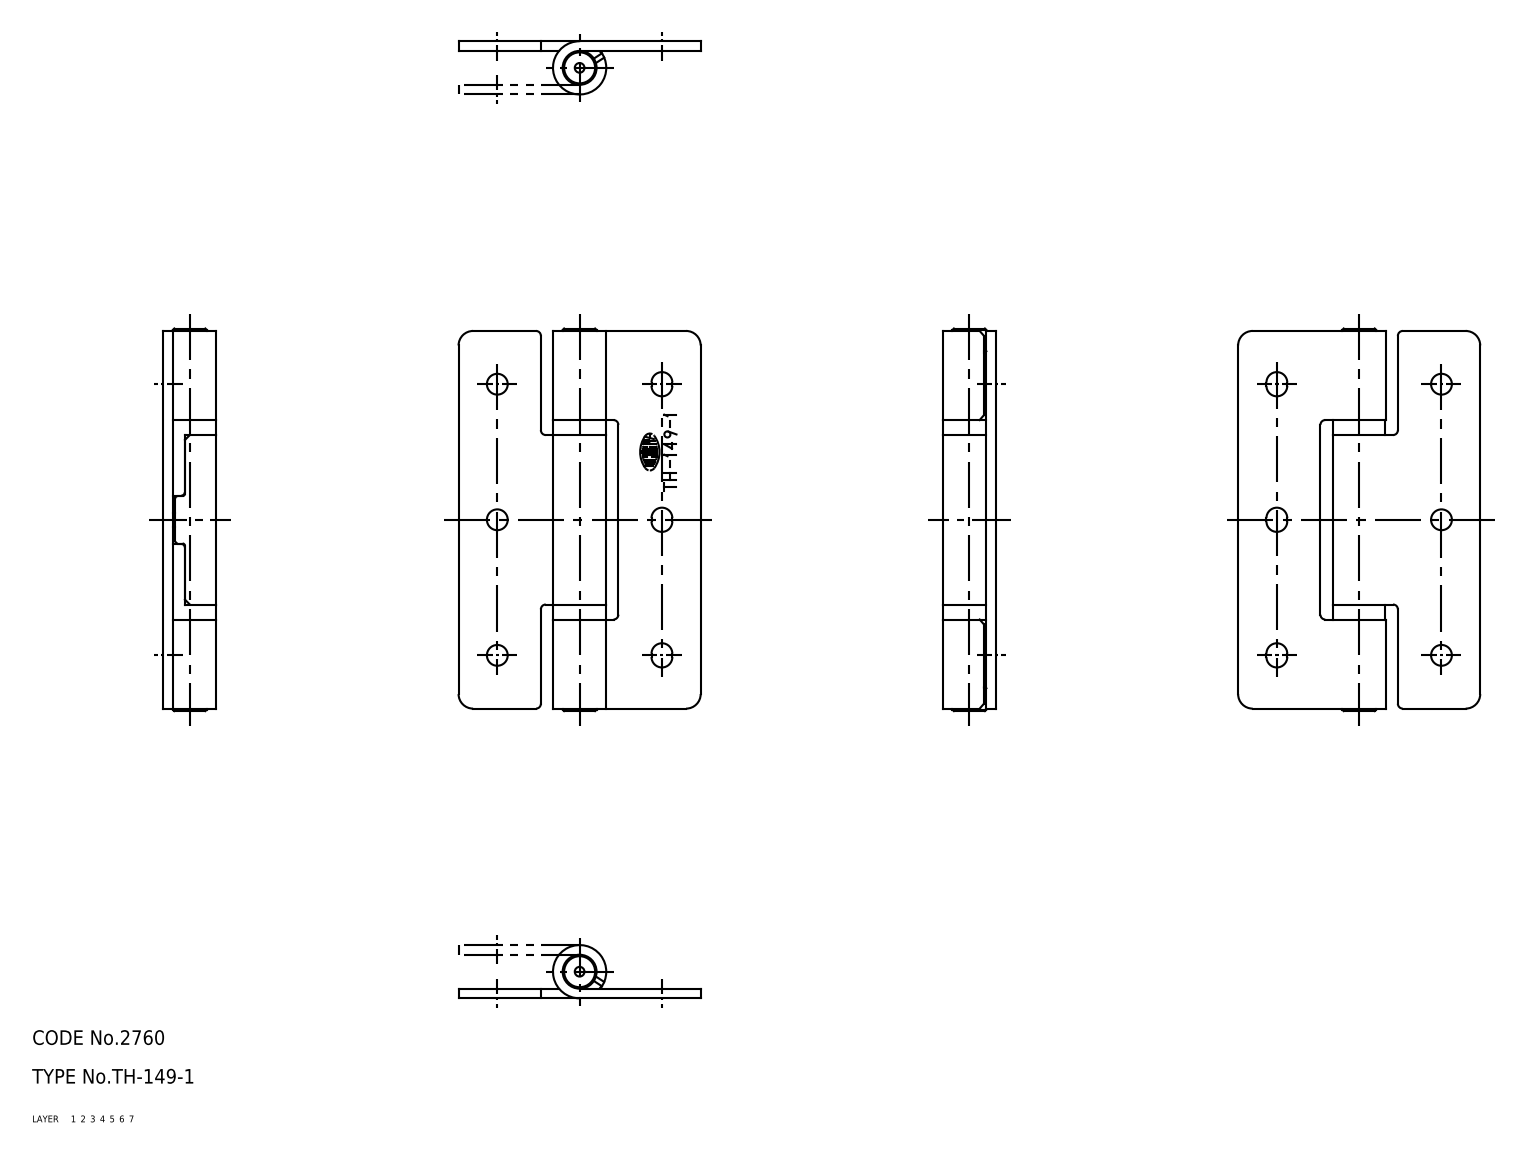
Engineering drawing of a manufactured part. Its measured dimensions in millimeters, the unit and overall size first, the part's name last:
Units: millimetres
Overall size (bounding box): 79 × 50 × 11
Volume: 12 678 mm³ · Surface area: 14 434 mm²
Bodies: 6 solids, 116 faces (0 planar, 0 cylindrical, 116 other)
Part name (STEP PRODUCT): 67115763; 67115776; 67115789; 67115802 (+2 more)
STEP written by: CADfix (AUTOMOTIVE_DESIGN)
